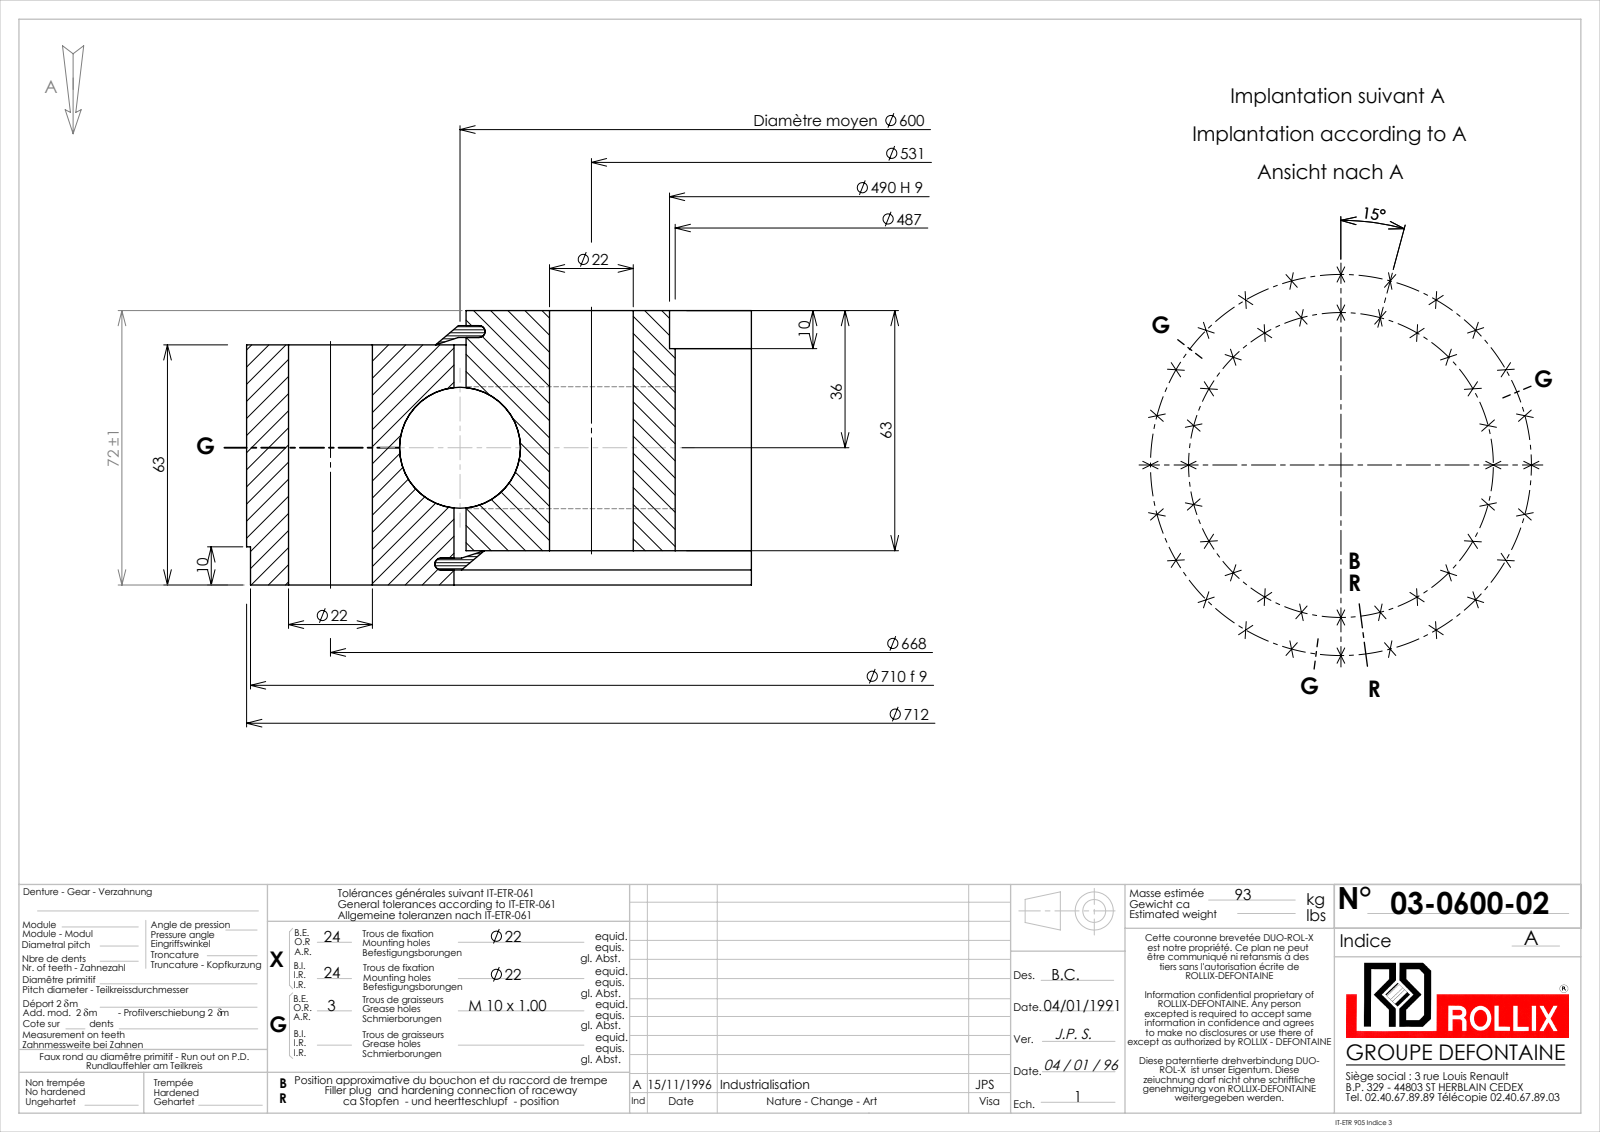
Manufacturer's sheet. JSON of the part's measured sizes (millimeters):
{"part_name": "03-0600-02", "step_written_by": "SolidWorks 2016 (CONFIG_CONTROL_DESIGN)", "units": "millimeters", "bodies": {"solids": 5, "faces": 164, "planar": 14, "cylindrical": 122, "other": 28}, "overall_size": [712, 712, 72], "volume_mm3": 10540000, "surface_area_mm2": 1268000, "round_holes": [[22, 48], [9, 3], [487, 1], [490, 1], [603.18, 1]], "round_bosses_or_shafts": [[712, 1], [710, 1], [596.83, 1]], "face_to_face_distances": [63, 9, 54, 72, 7.05, 64.95, 1.95, 55.95, 3.95, 68.05], "hole_center_spacings": [265.5, 421.27, 459.86, 490.58, 137.43, 375.47, 512.91, 69.31]}
